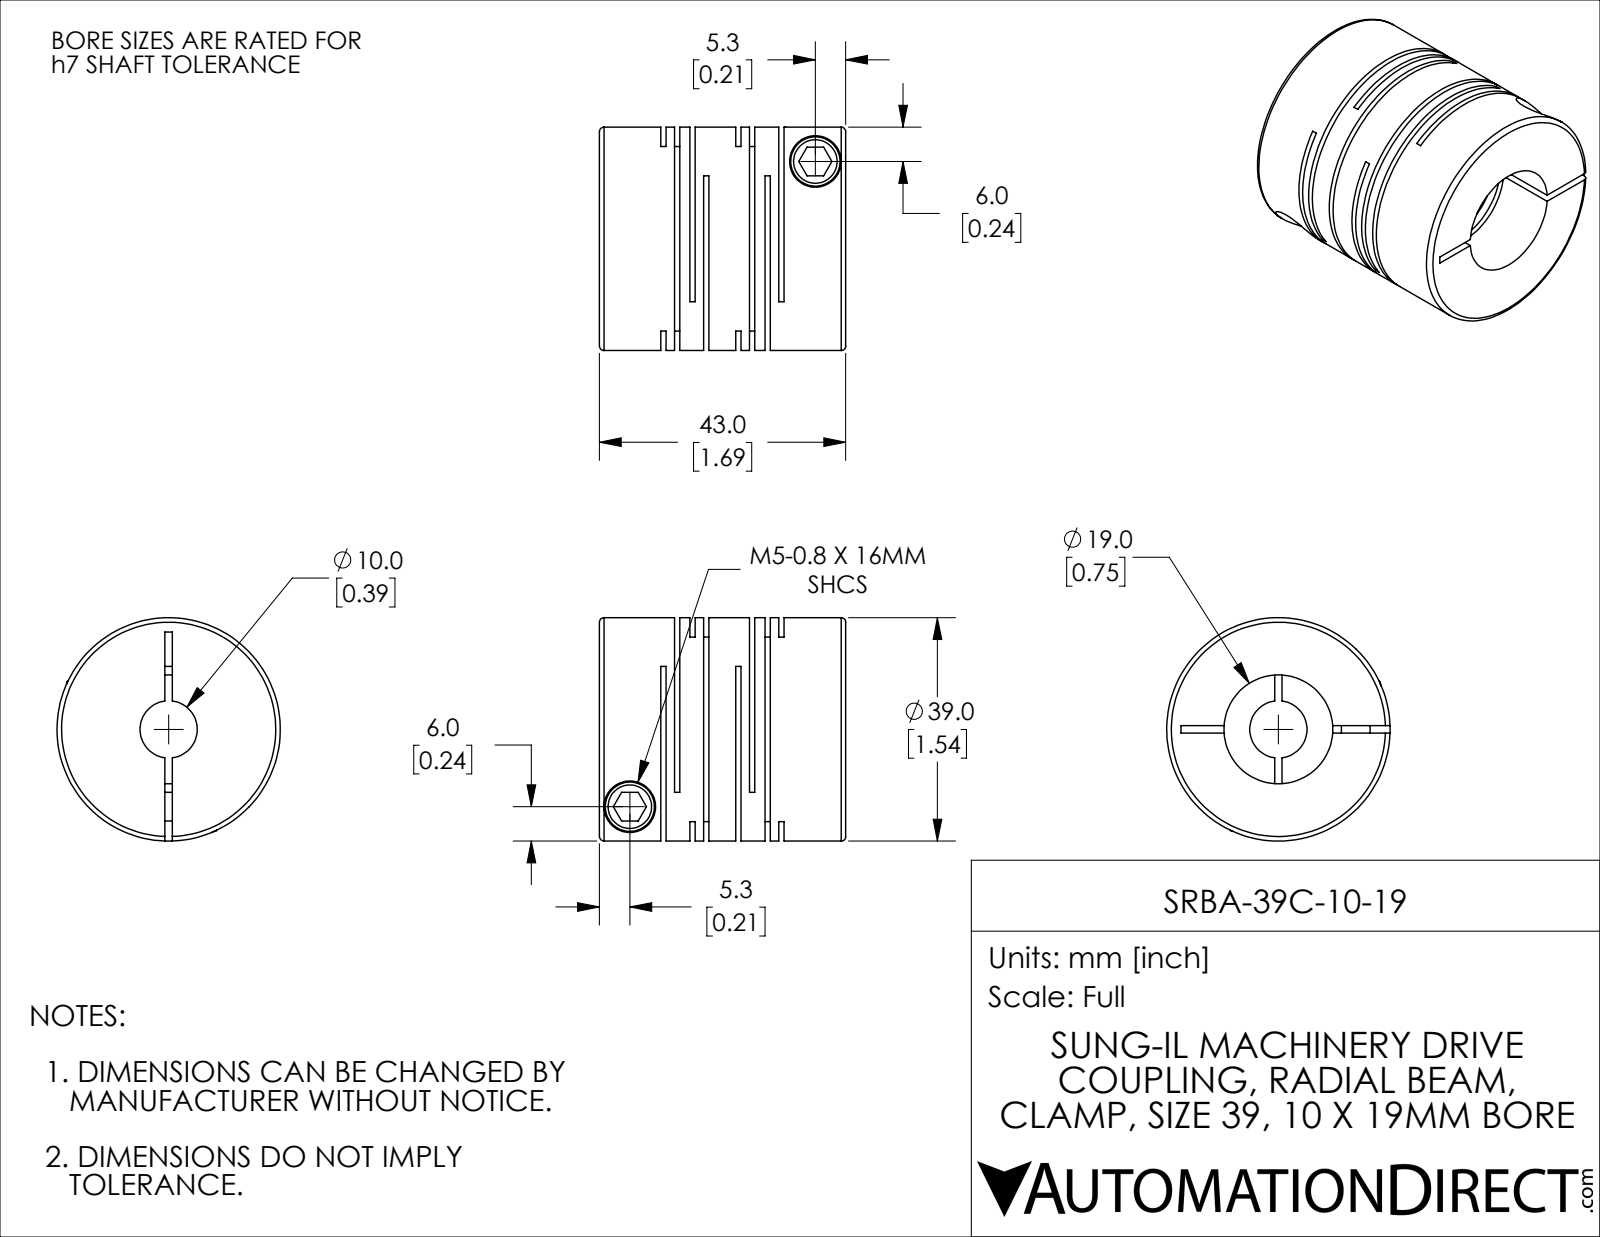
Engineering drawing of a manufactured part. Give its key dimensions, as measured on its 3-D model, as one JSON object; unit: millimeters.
{"part_name": "SRBA-39C-10-19", "step_written_by": "SolidWorks 2021 (CONFIG_CONTROL_DESIGN)", "units": "millimeters", "bodies": {"solids": 1, "faces": 114, "planar": 60, "cylindrical": 42, "other": 12}, "overall_size": [43, 39, 39], "volume_mm3": 34556, "surface_area_mm2": 21952, "round_holes": [[5, 2], [9, 2], [10, 1], [19, 1]], "round_bosses_or_shafts": [[8.6, 2], [39, 1]], "face_to_face_distances": [13.1, 0.92, 2.4, 5.1, 10.7, 14.02, 18.2, 3.32, 15.5, 1.48]}
